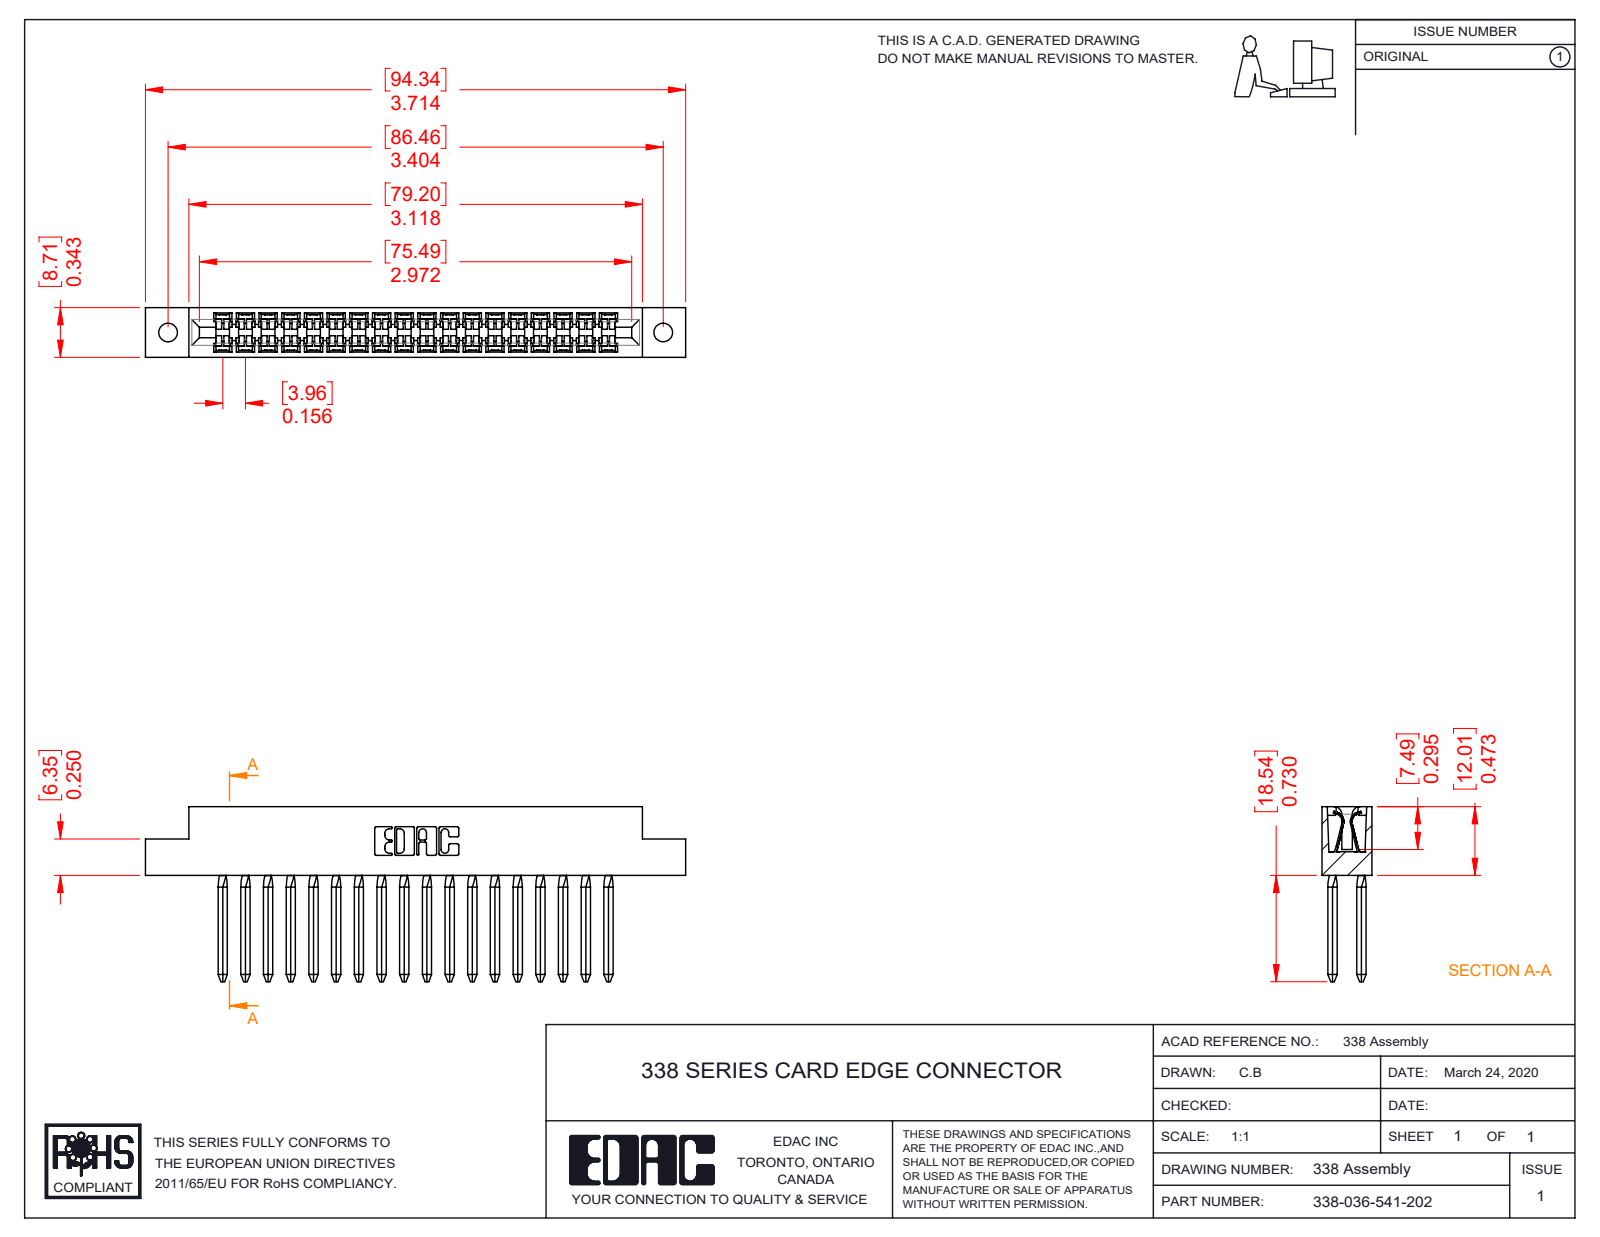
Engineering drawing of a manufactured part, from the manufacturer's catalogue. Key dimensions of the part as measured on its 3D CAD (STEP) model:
Part name (STEP PRODUCT): 338-290-001_541; 338-036-541-202; 338-210-001_338-210-018-002
STEP written by: SolidWorks 2016 (CONFIG_CONTROL_DESIGN)
Units: inches
Bodies: 37 solids, 2506 faces (1742 planar, 620 cylindrical, 144 other)
Overall size (bounding box): 3.714 × 1.203 × 0.343
Volume: 0.437 in³ · Surface area: 19.78 in²
Round holes (diameter × count): ⌀0.128 ×2
Partial cylindrical surfaces — rounded edges, fillets, slot ends (radius × count): R0.025 ×110, R0.008 ×36, R0.055 ×30, R0.067 ×30, R0.1 ×28, R0.01 ×22, R0.007 ×6, R0.031 ×6
Main face-to-face distances: 0.343, 0.156, 0.624, 0.11, 0.78, 0.468, 0.135, 0.207, 0.221, 0.312
Hole centre spacings: 3.404
